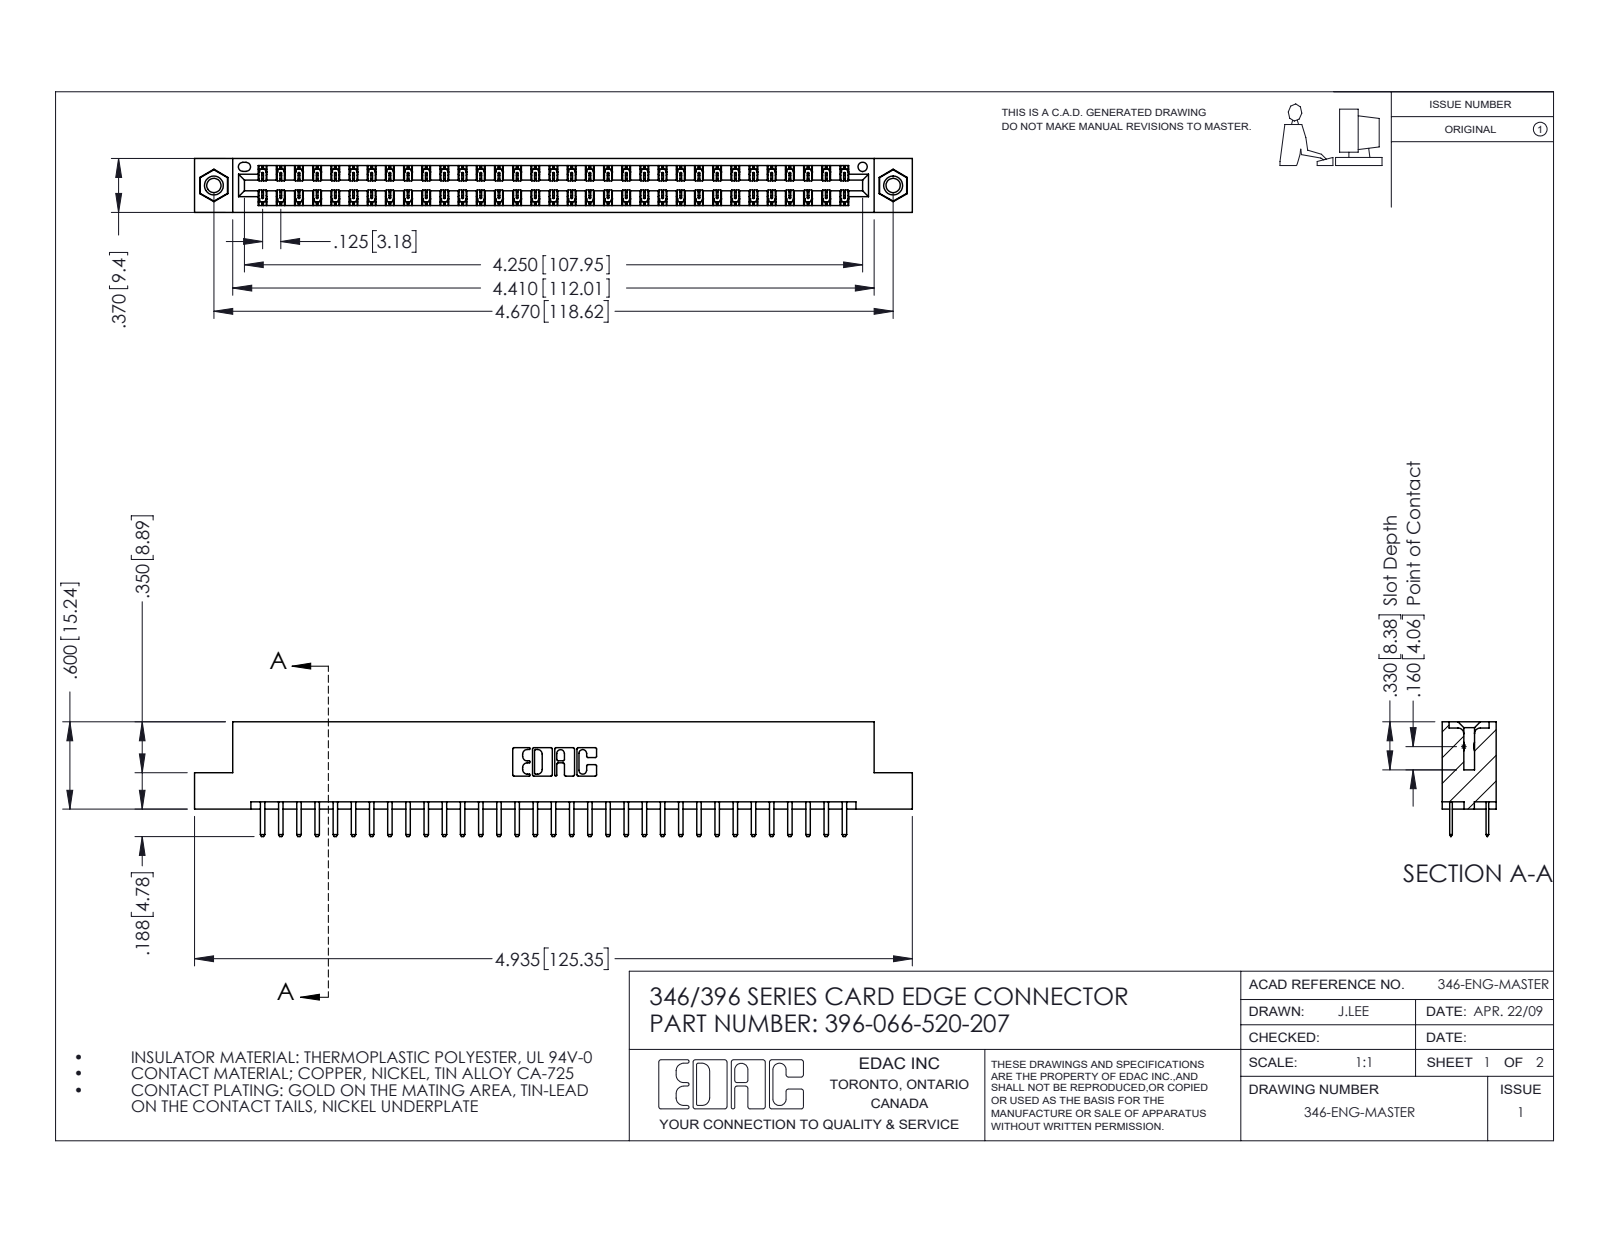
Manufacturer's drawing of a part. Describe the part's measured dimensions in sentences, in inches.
The part is named "396-066-520-207; 345-250-001_345-250-005-103; 346 Part_Flush Mounting Lugs - 0.156 Dia-TI; 345-292-001_345-293-120". Its 3-D file was written by "SolidWorks 2016 (CONFIG_CONTROL_DESIGN)". It is 69 solids with 3878 faces: 2550 planar, 1312 cylindrical and 16 other. Overall it measures 4.935 by 0.788 by 0.37 inches. Its volume is 0.739 cubic inches and its surface area 25.53 square inches. Round holes: 2 of diameter 0.098, 2 of diameter 0.125, 2 of diameter 0.156, 1 of diameter 0.064. Round bosses or shafts: 2 of diameter 0.155. Partial cylindrical surfaces (rounded edges, fillets, slot ends): 99 of radius 0.006, 70 of radius 0.01, 22 of radius 0.01, 6 of radius 0.007, 6 of radius 0.031, 3 of radius 0.026, 2 of radius 0.014, 2 of radius 0.022. The main face-to-face distances are 0.048, 0.322, 0.25, 0.37, 0.275, 0.072, 0.298, 0.025, 0.148, 0.222. The hole center spacings are 0.246, 4.462, 4.67.
